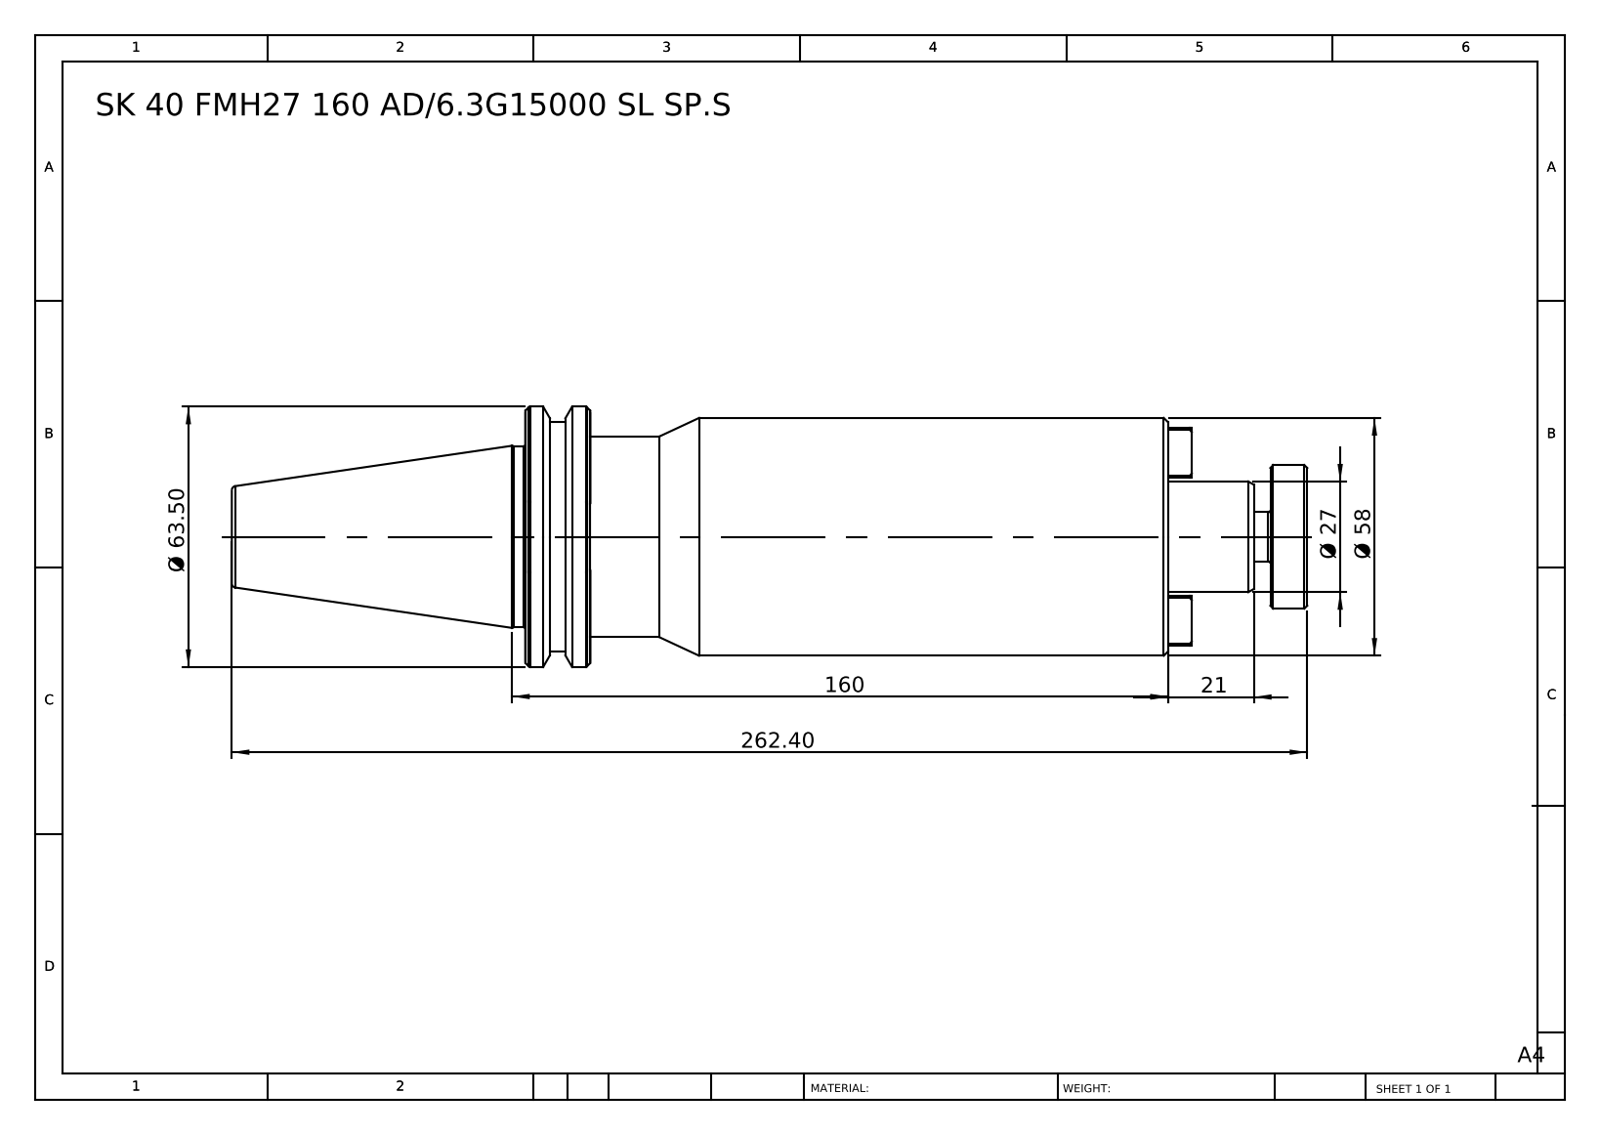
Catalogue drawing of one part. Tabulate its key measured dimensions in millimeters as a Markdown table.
| quantity | value |
| --- | --- |
| part name | SK40 FMH27 160 AD-6.3G15000 SL SP.S |
| STEP written by | SolidWorks 2014 (CONFIG_CONTROL_DESIGN) |
| units | millimeters |
| bodies | 1 solid, 109 faces (35 planar, 18 cylindrical, 56 other) |
| overall size | 262.4 × 63.5 × 63.5 |
| volume | 495 514 mm³ |
| surface area | 47 816 mm² |
| round bosses / shafts (diameter × count) | 63.5 × 1, 58 × 1, 56 × 1, 49 × 1, 44 × 1, 35 × 1, 27 × 1, 12 × 1 |
| main face-to-face distances | 156.8, 140.9, 15.9, 34, 174.9, 190.8, 9, 25, 165.9, 181.8 |
